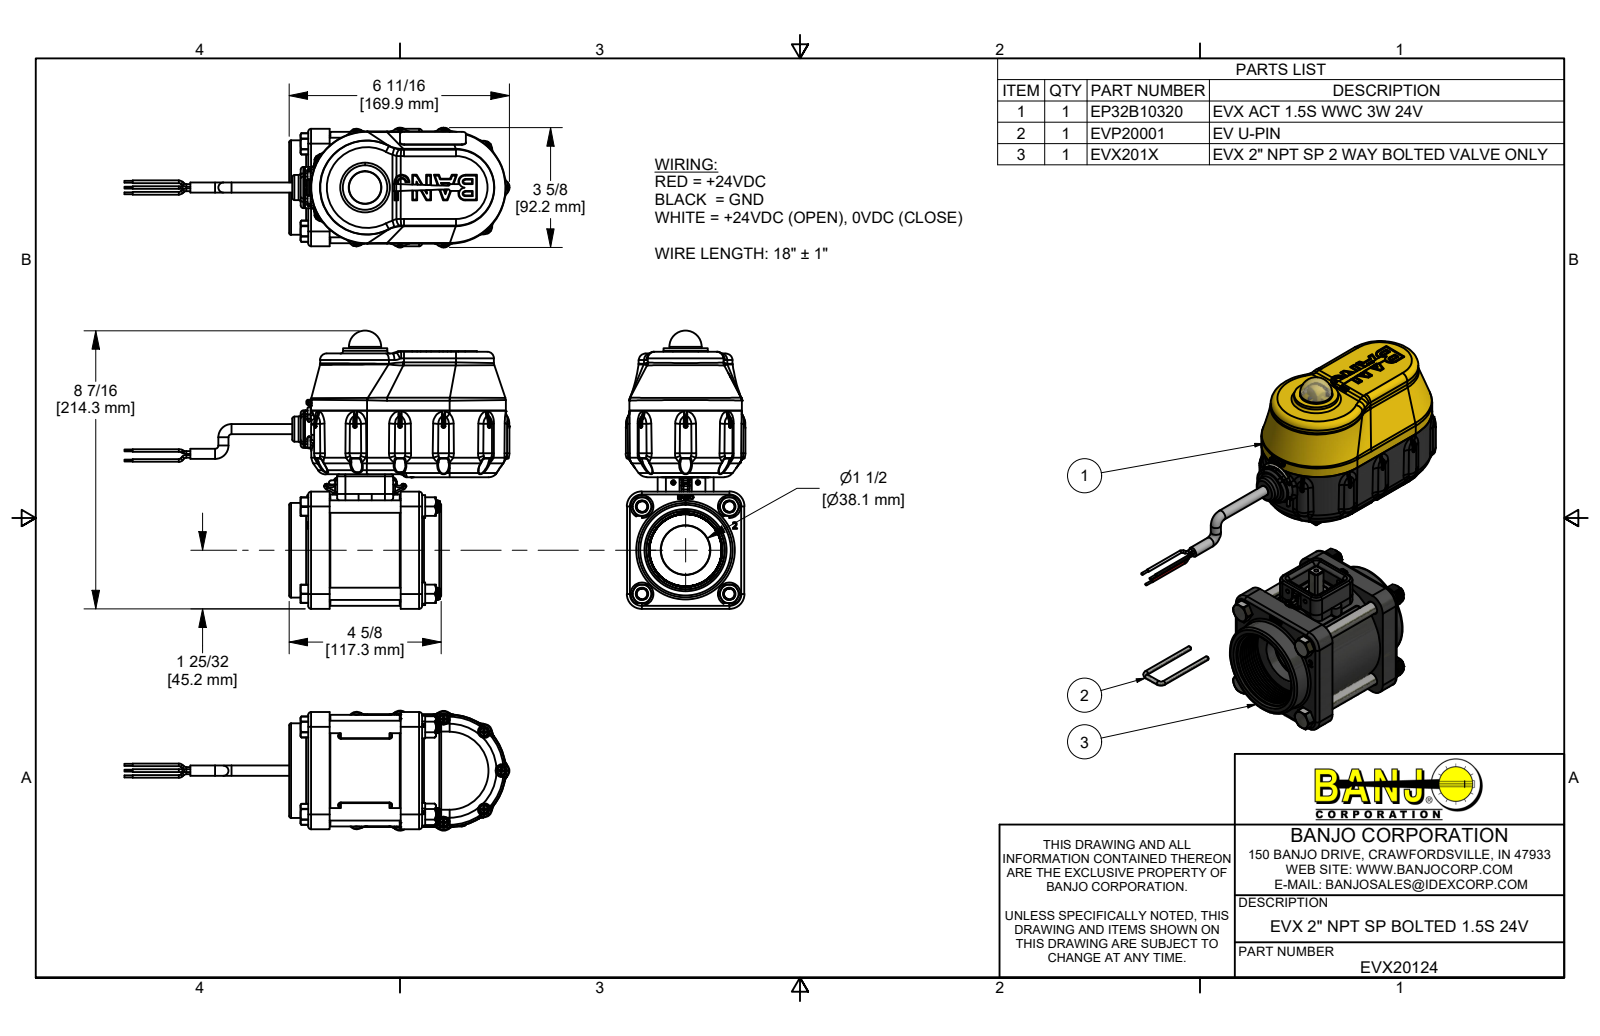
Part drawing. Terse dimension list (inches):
name: EVX20124; EP32B10320; B61905PPHS; B632038PM (+8 more)
written by: Autodesk Inventor 2021 (AUTOMOTIVE_DESIGN)
unit: in
bodies: 96 solids, 11498 faces (2928 planar, 3381 cylindrical, 5189 other)
size: 11.685 × 8.437 × 3.63
volume: 59.77 in³; area: 660.8 in²
holes: 11× ⌀0.095, 11× ⌀0.15, 7× ⌀0.08, 4× ⌀0.107, 4× ⌀0.126, 4× ⌀0.136, 4× ⌀0.148, 4× ⌀0.15, 4× ⌀0.17, 4× ⌀0.307, 4× ⌀0.385, 4× ⌀0.42
bosses: 60× ⌀0.324, 17× ⌀0.25, 15× ⌀0.08, 11× ⌀0.14, 11× ⌀0.108, 11× ⌀0.085, 6× ⌀0.058, 5× ⌀0.375
rounds: 180× R0.013, 145× R0.04, 100× R0.02, 94× R0.01, 57× R0.005, 39× R0.03, 37× R0.015, 28× R0.06
face distances: 0.1, 2.565, 0.06, 0.65, 2.808, 0.729, 0.211, 0.151, 1.896, 1.836
hole spacings: 1.872, 2.648, 2.69, 2.715, 1.662, 1.774, 2.088, 2.73
